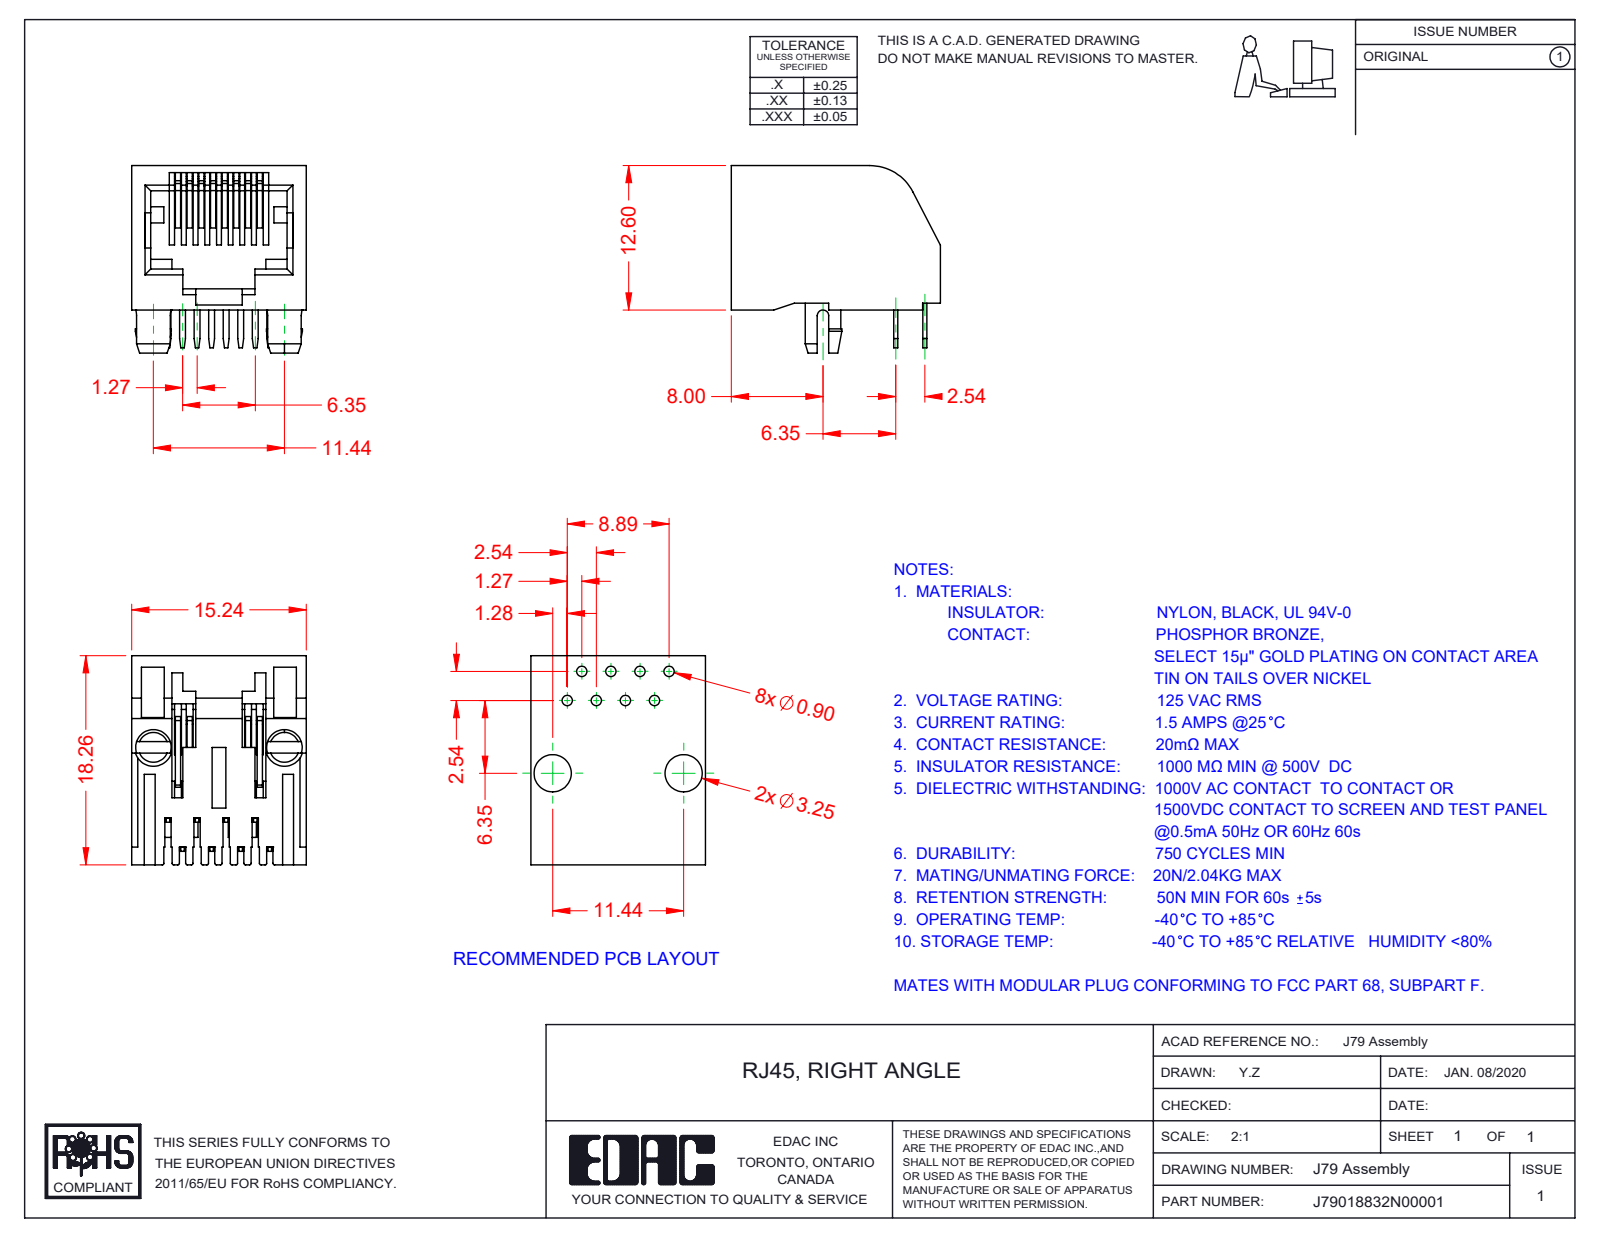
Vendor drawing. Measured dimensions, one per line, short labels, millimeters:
name: RJ79018832N00001; 79 Contacts; 79 Insulator
written by: SolidWorks 2016 (CONFIG_CONTROL_DESIGN)
unit: mm
bodies: 9 solids, 574 faces (424 planar, 144 cylindrical, 6 other)
size: 18.26 × 16.36 × 15.24
volume: 1 496 mm³; area: 3 263 mm²
bosses: 2× ⌀3.1
rounds: 16× R0.15, 7× R0.5, 3× R0.72, 2× R0.36, 2× R1.65, 2× R1.8, 2× R2.16, 1× R0.2
face distances: 15.24, 2.04, 0.6, 12, 0.36, 4.08, 1.25, 9.8, 2.2, 8.2
